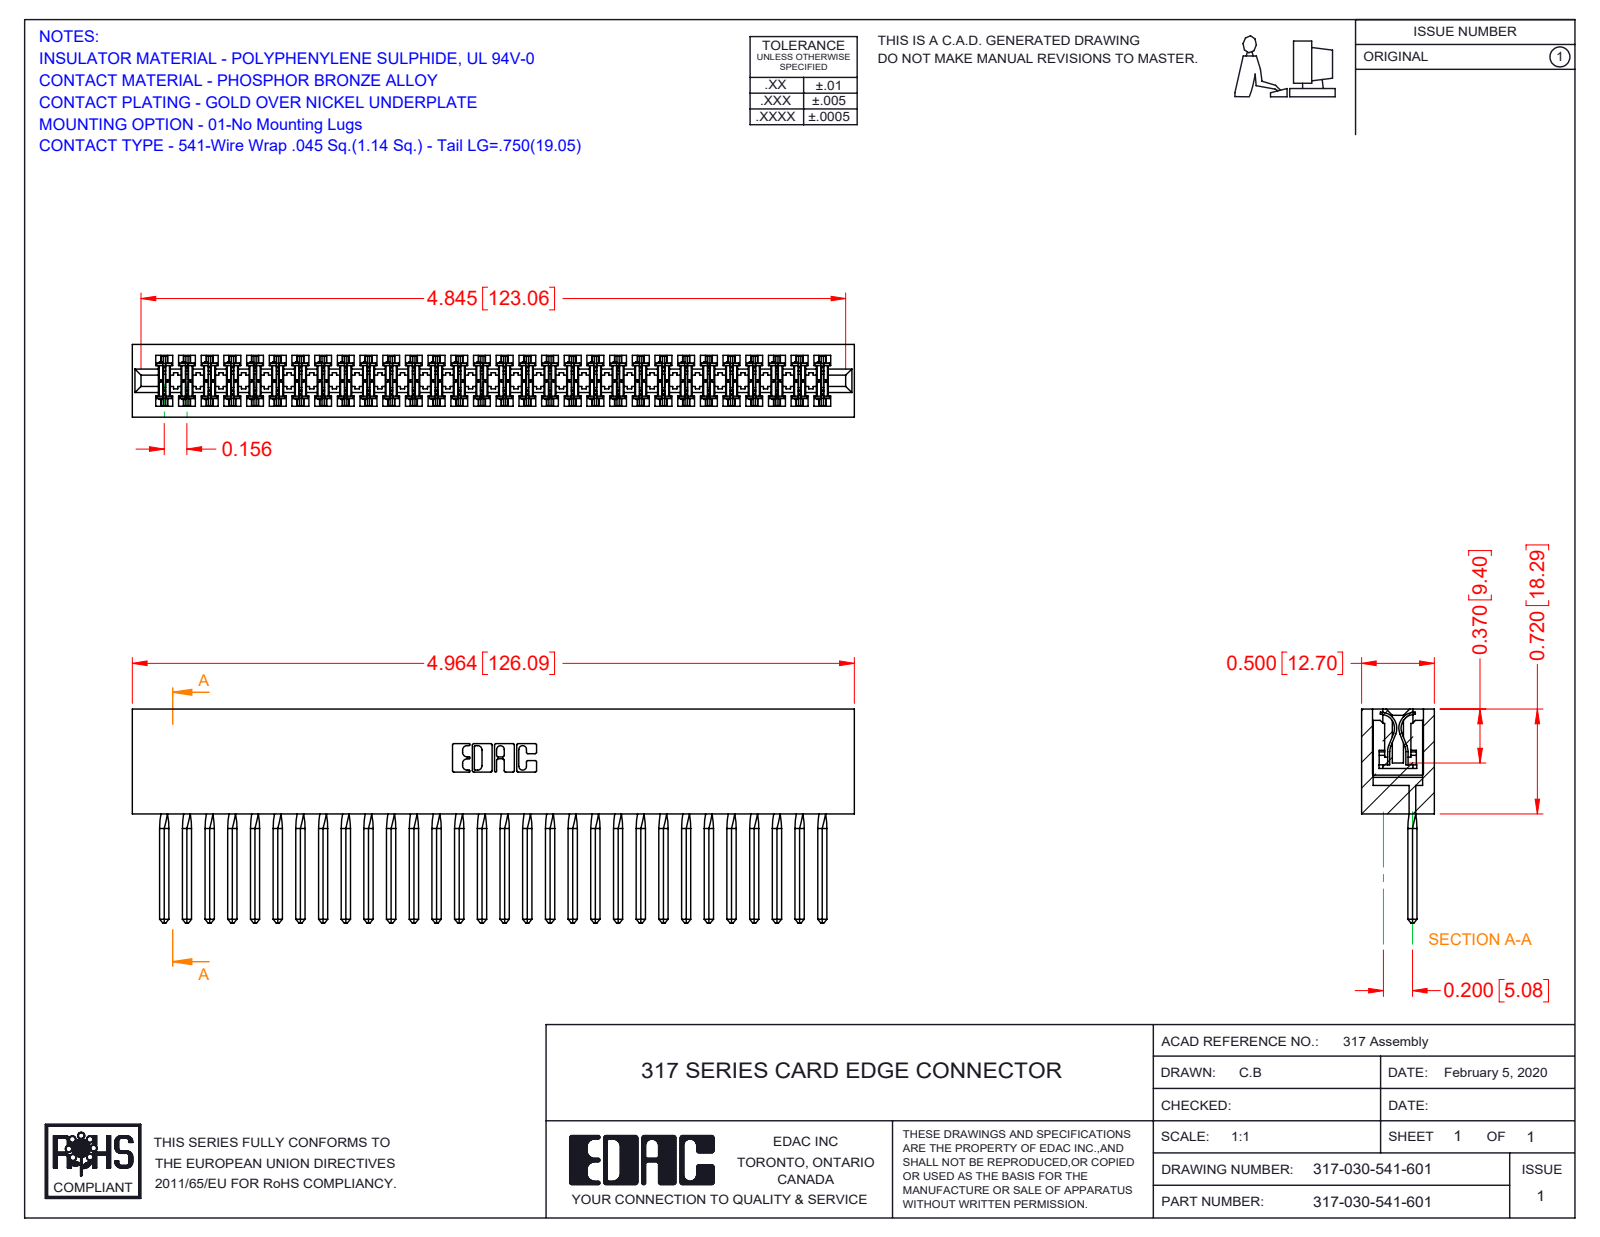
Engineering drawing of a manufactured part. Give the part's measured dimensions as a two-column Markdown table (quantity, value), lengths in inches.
| quantity | value |
| --- | --- |
| part name | 317-290-002_541; 317 Part_Lugless; 317-030-541-601 |
| STEP written by | SolidWorks 2016 (CONFIG_CONTROL_DESIGN) |
| units | inches |
| bodies | 31 solids, 4650 faces (3770 planar, 760 cylindrical, 120 other) |
| overall size | 4.964 × 1.47 × 0.5 |
| volume | 1.329 in³ |
| surface area | 47.39 in² |
| partial cylindrical surfaces (radius × count) | 0.015 × 60, 0.01 × 22, 0.007 × 6, 0.031 × 6, 0.026 × 3, 0.095 × 2, 0.1 × 2, 0.11 × 2 |
| main face-to-face distances | 0.075, 0.5, 0.425, 0.35, 0.11, 0.195, 0.72, 0.115, 0.211, 0.289 |
